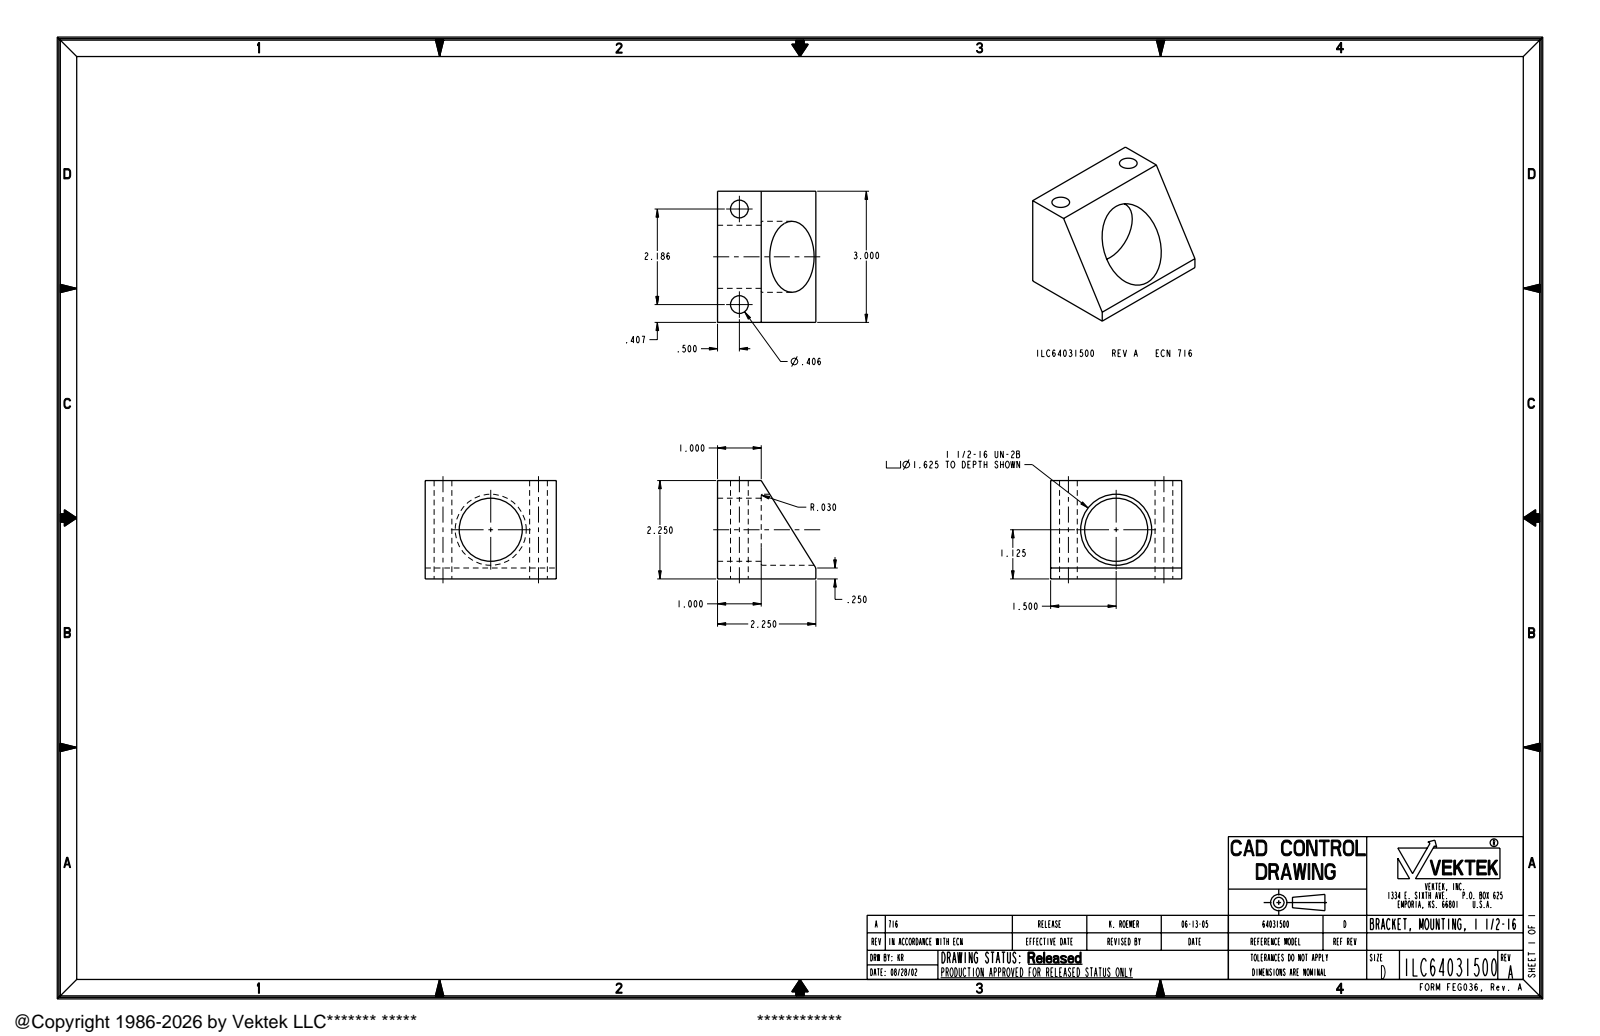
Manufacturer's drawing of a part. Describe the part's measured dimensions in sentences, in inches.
The part is named "ILC64031500". Its 3-D file was written by "PRO/ENGINEER BY PARAMETRIC TECHNOLOGY CORPORATION, 2004290 (AUTOMOTIVE_DESIGN_CC2)". It is 1 solid with 18 faces: 8 planar, 8 cylindrical and 2 other. Overall it measures 3 by 2.25 by 2.25 inches. Its volume is 7.762 cubic inches and its surface area 41.59 square inches. Round holes: 2 of diameter 0.406, 1 of diameter 1.443, 1 of diameter 1.625. The main face-to-face distances are 3, 2.25, 1.25, 1. The hole center spacings are 2.186.
